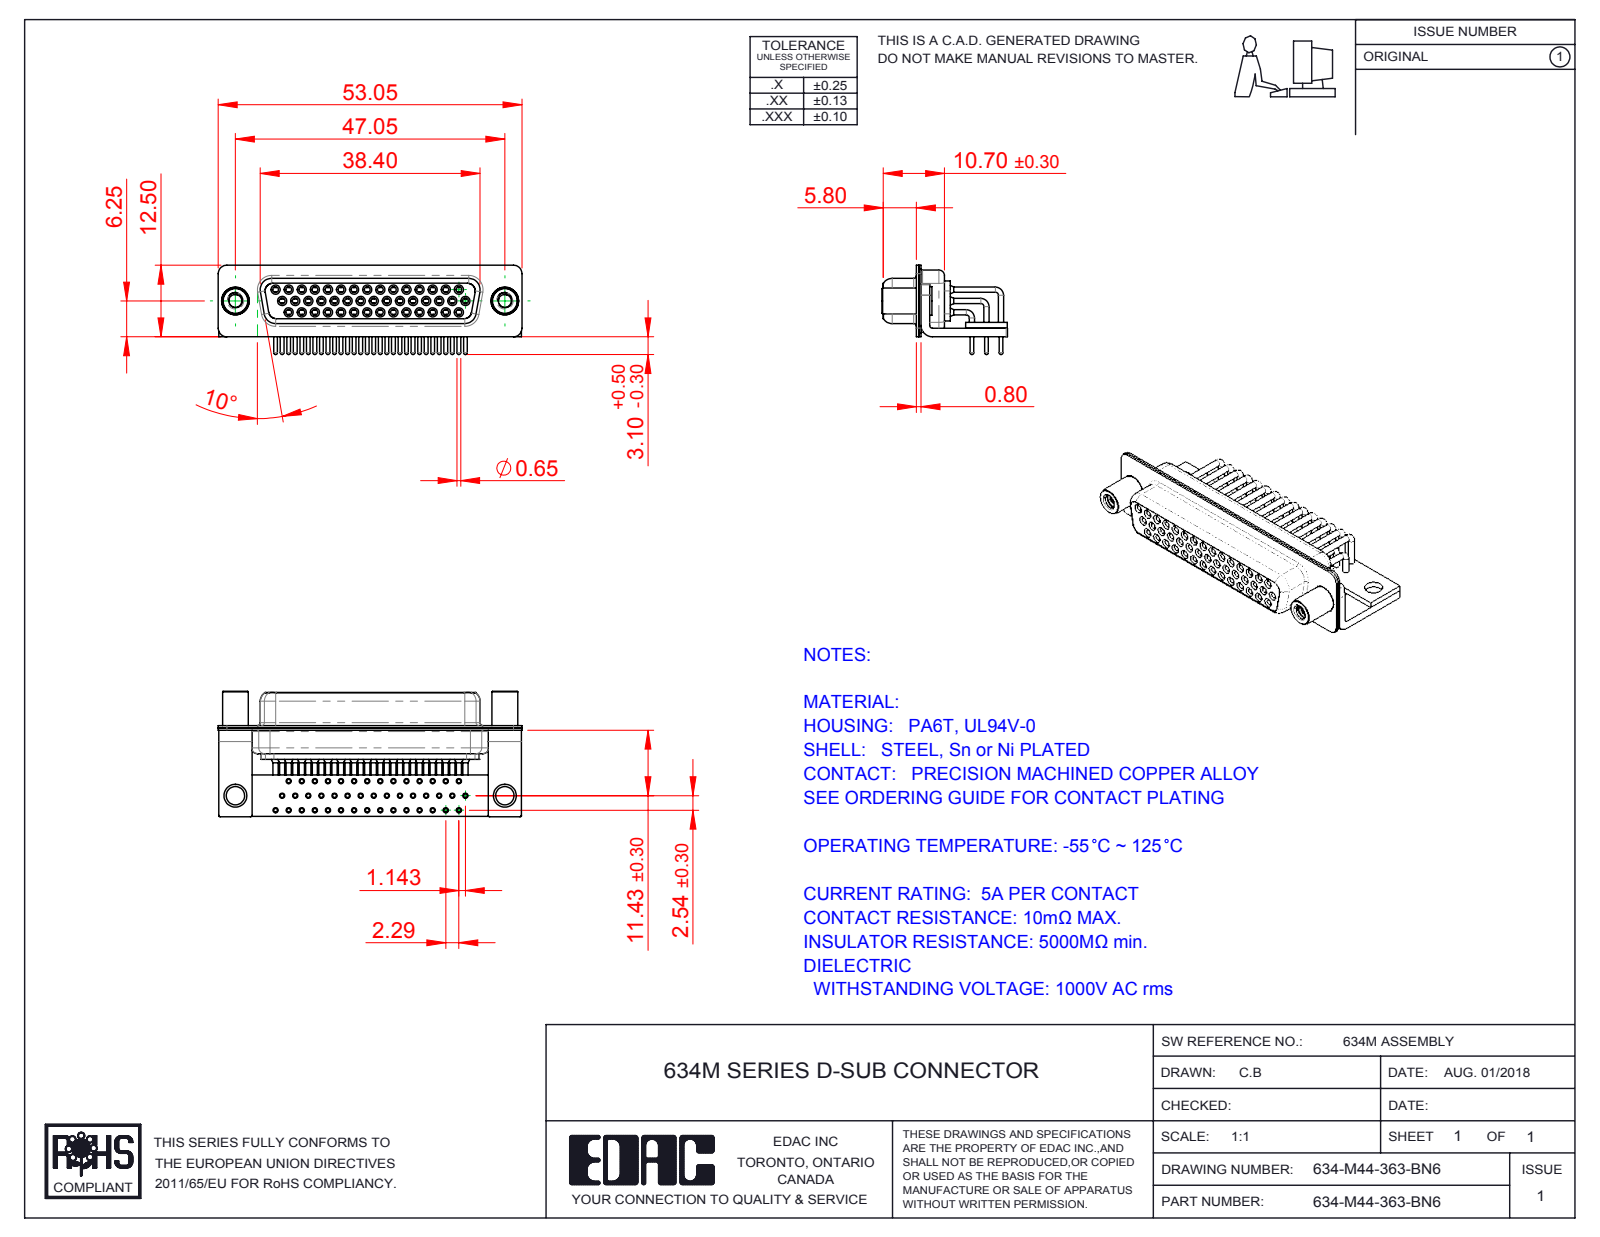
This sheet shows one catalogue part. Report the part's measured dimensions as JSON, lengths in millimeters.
{"part_name": "634M Shell Front_44 Contacts; 634-M44-363-BN6; 634M Housing_44 Contacts; 634M 4-40 Threaded Standoff (+6 more)", "step_written_by": "SolidWorks 2016 (CONFIG_CONTROL_DESIGN)", "units": "millimeters", "bodies": {"solids": 52, "faces": 2799, "planar": 755, "cylindrical": 1301, "other": 743}, "overall_size": [53.05, 21.9, 15.6], "volume_mm3": 4584, "surface_area_mm2": 14913, "round_holes": [[0.9, 44], [1, 44], [1.1, 44], [1.7, 44], [1.8, 44], [2, 44], [2.26, 2], [3.2, 2], [4, 2], [4.8, 2]], "round_bosses_or_shafts": [[1.6, 44], [1.5, 44], [0.9, 44], [0.65, 44], [5, 2], [4.9, 2], [4.5, 2]], "partial_cylinders_radius": [[0.25, 16], [1.5, 16], [2, 13], [1.35, 8], [1.6, 8], [0.5, 5], [0.6, 4], [0.65, 4]], "face_to_face_distances": [0.4, 2.3, 1.9, 1, 0.8, 8.5, 9.35, 1.45, 8.95, 1.5], "hole_center_spacings": [2.28, 2.29, 4.57, 6.86, 11.43, 3.96, 8.24, 9.14]}
